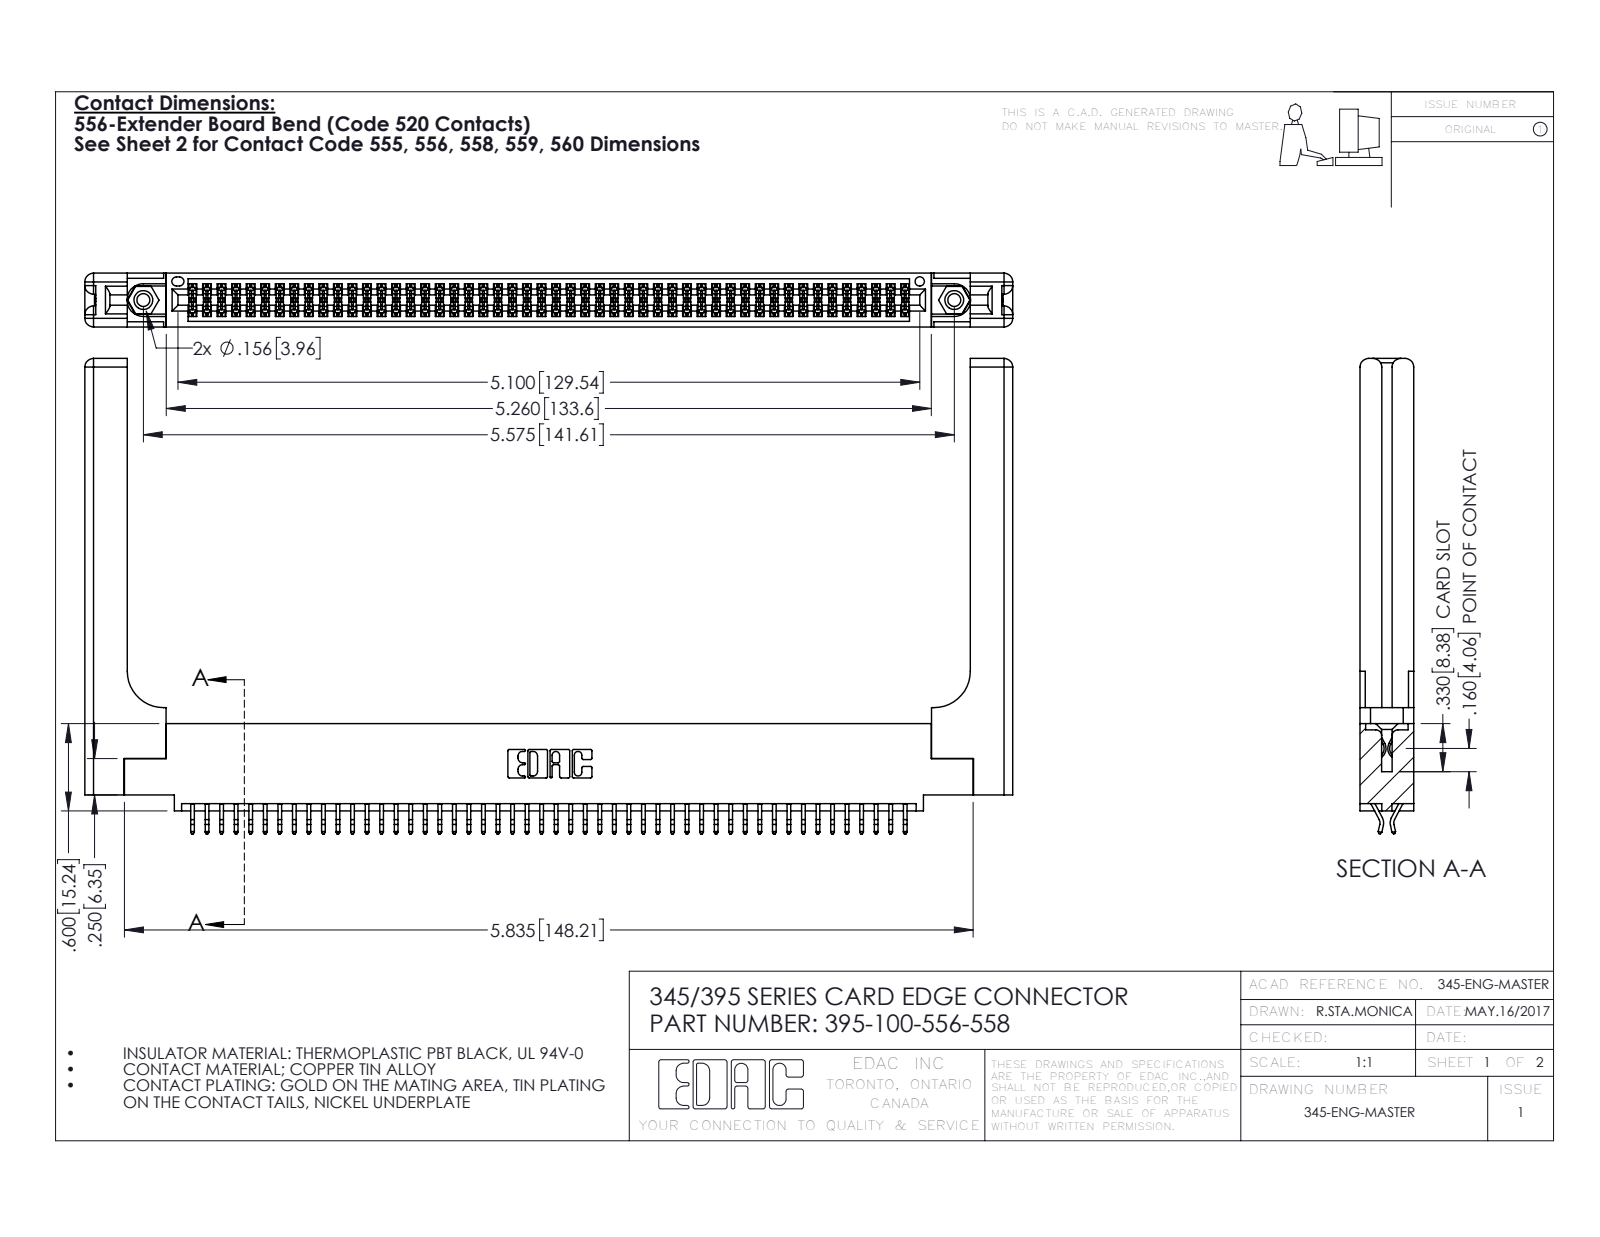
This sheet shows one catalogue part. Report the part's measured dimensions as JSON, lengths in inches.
{"part_name": "345 Part_0.110 Offset - 0.156 Dia-TH; 345-250-001_345-250-001-102; 395-100-556-558; 345-220-058_345-220-058 (+1 more)", "step_written_by": "SolidWorks 2016 (CONFIG_CONTROL_DESIGN)", "units": "inches", "bodies": {"solids": 105, "faces": 5986, "planar": 3932, "cylindrical": 1994, "other": 60}, "overall_size": [6.379, 3.267, 0.37], "volume_in3": 1.477, "surface_area_in2": 44.14, "round_holes": [[0.089, 2], [0.125, 2], [0.156, 2], [0.064, 1]], "round_bosses_or_shafts": [[0.155, 2]], "partial_cylinders_radius": [[0.006, 150], [0.01, 22], [0.06, 16], [0.007, 6], [0.031, 6], [0.026, 3], [0.01, 2], [0.014, 2]], "face_to_face_distances": [0.072, 0.37, 0.298, 0.025, 0.098, 0.272, 0.2, 0.225, 0.148, 0.15], "hole_center_spacings": [0.27, 5.339, 5.575]}
